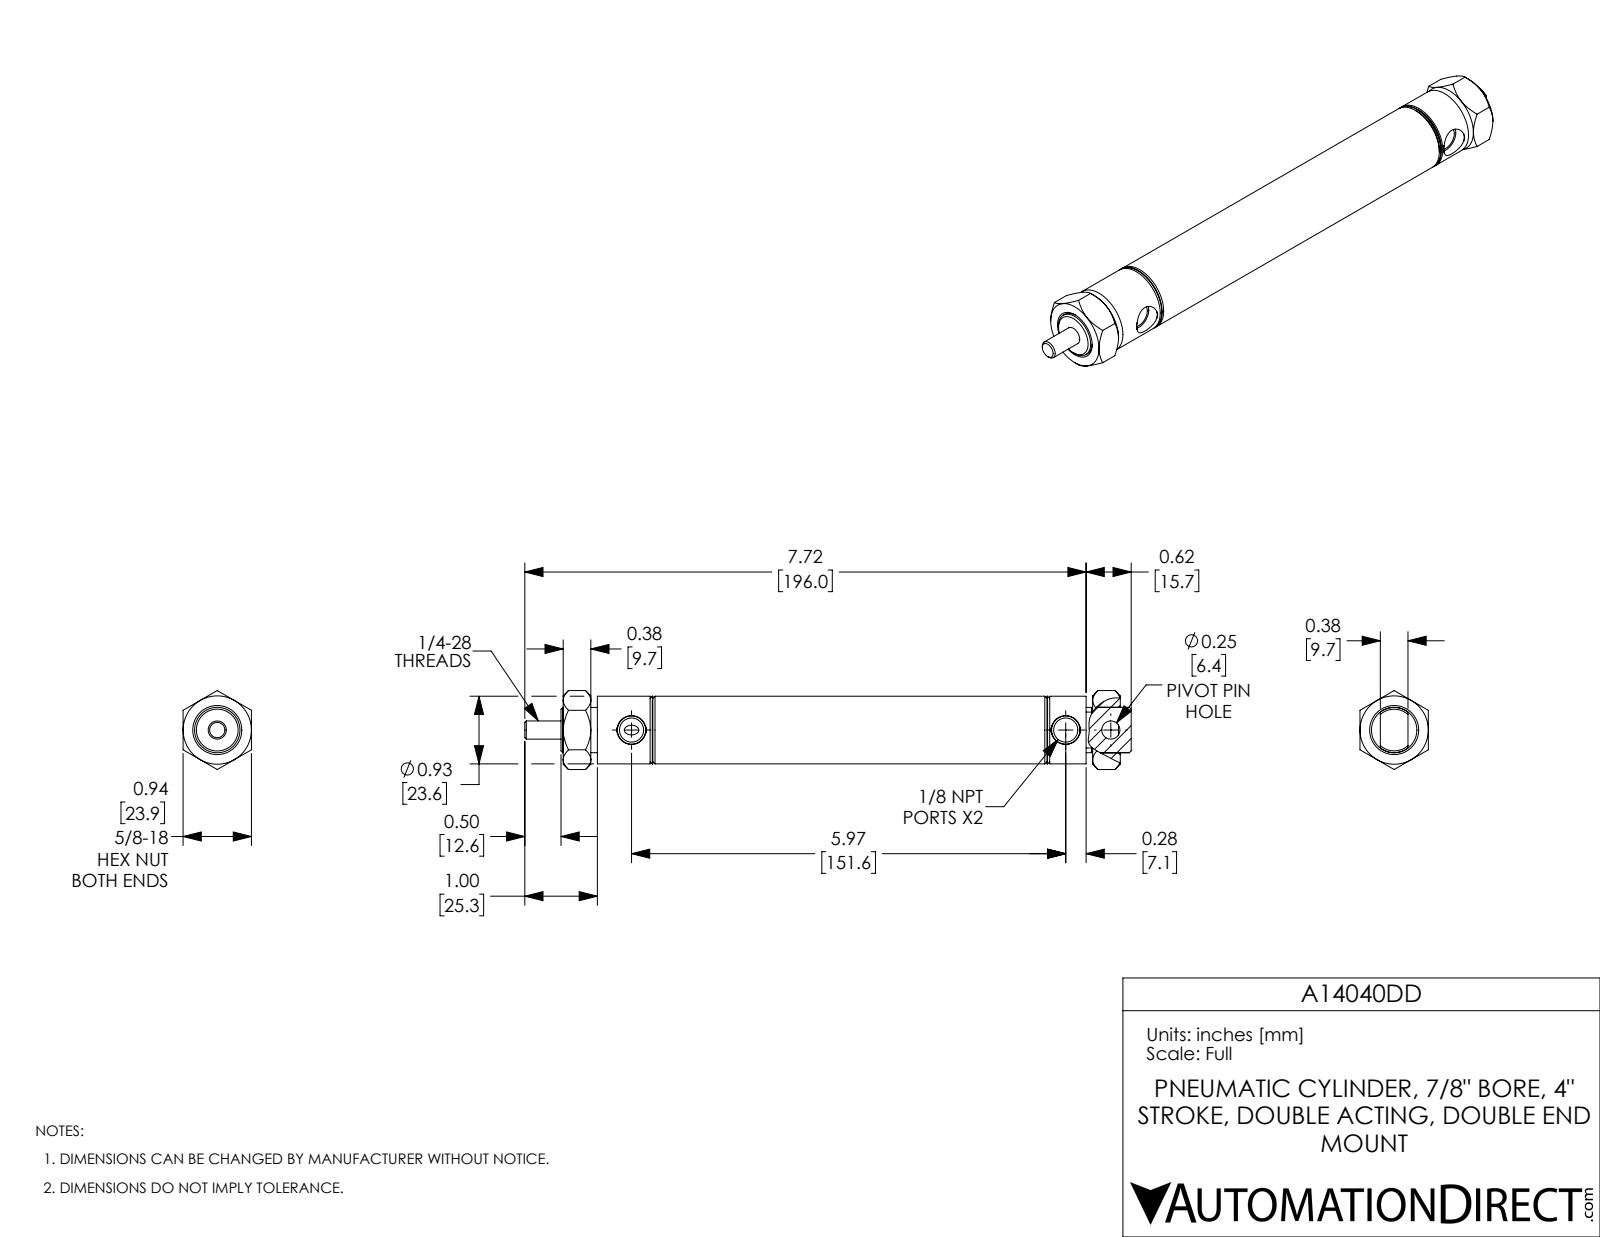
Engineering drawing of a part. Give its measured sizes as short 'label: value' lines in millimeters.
name: A14040DD_Mounting Nut_D-9; A14040DD-MainBody; A14040DD; A14040DD-Rod
written by: SolidWorks 2017 (AUTOMOTIVE_DESIGN)
unit: mm
bodies: 4 solids, 137 faces (35 planar, 38 cylindrical, 64 other)
size: 211.8 × 27.6 × 23.9
volume: 47 780 mm³; area: 33 680 mm²
holes: 2× ⌀6.4, 2× ⌀8.4, 1× ⌀15.9, 1× ⌀22.2
bosses: 1× ⌀23.6, 1× ⌀15.8, 1× ⌀14.3
face distances: 23.9, 12.7, 11.9, 182.6, 9.7, 145.3, 25.3, 114.3, 101.6, 7.1
hole spacings: 15.7, 151.6, 167.4
